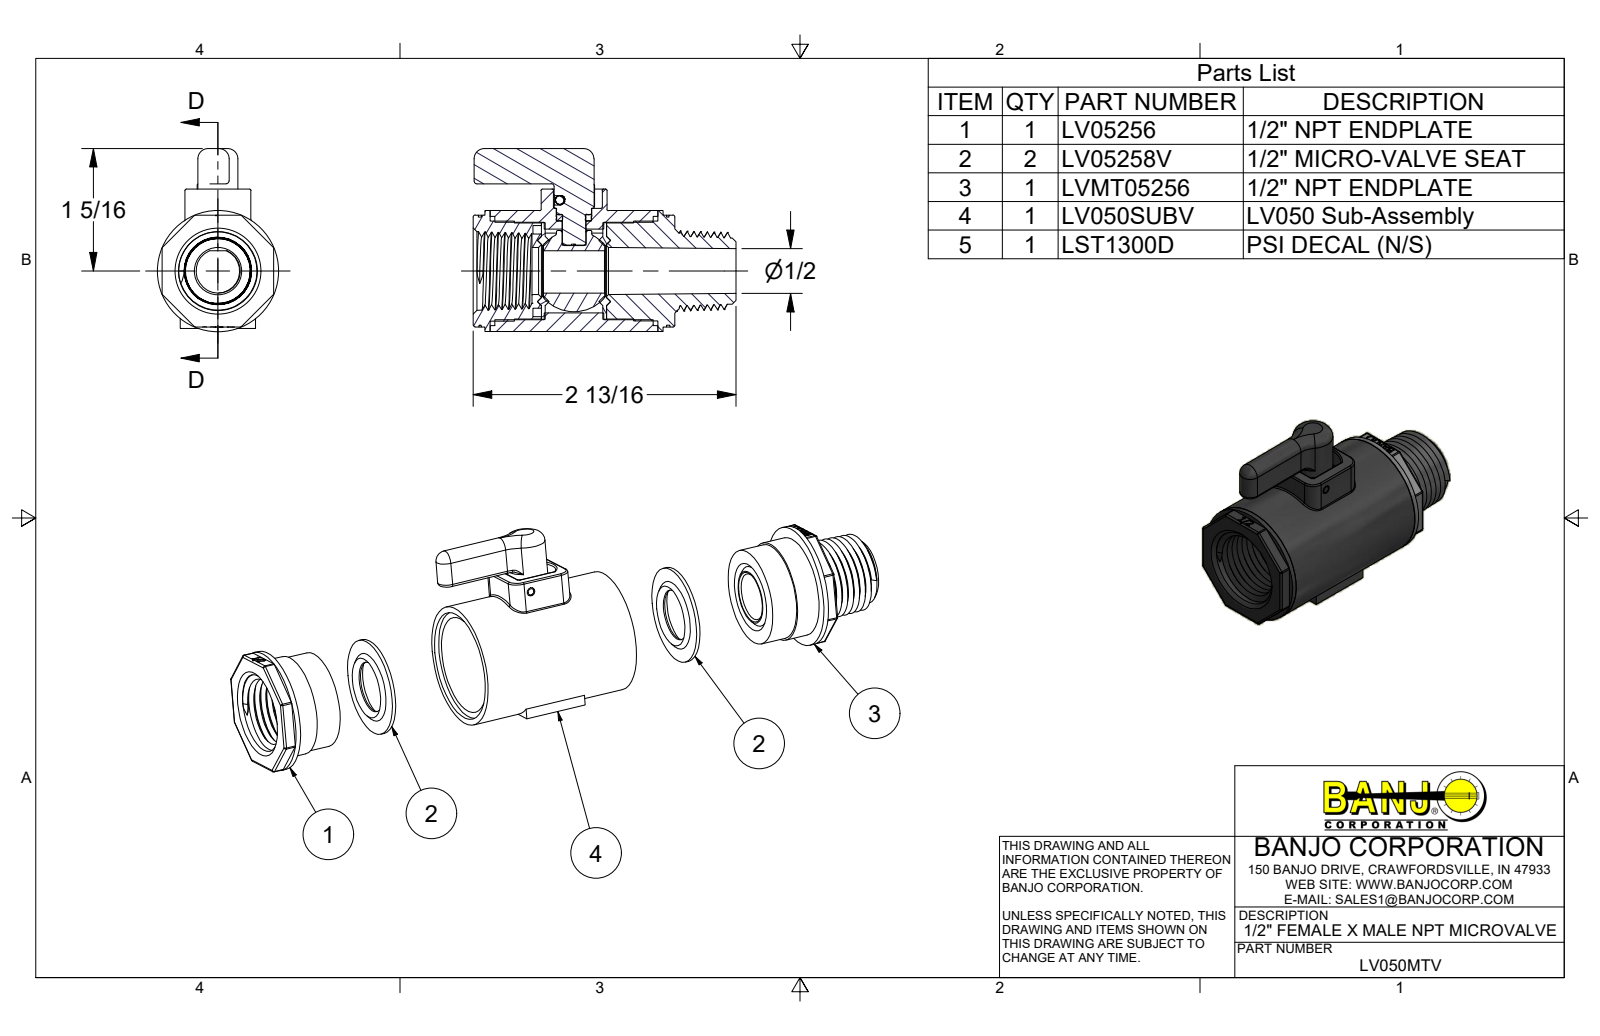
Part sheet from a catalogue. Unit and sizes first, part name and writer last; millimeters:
Units: millimetres
Overall size (bounding box): 70.9 × 49.4 × 32.6
Round holes (diameter × count): ⌀2.3 ×4, ⌀2.4 ×1, ⌀6.4 ×1, ⌀9.3 ×1, ⌀9.6 ×1, ⌀11.9 ×1, ⌀12.7 ×1, ⌀13.7 ×1, ⌀22.6 ×1, ⌀26.3 ×1, ⌀29.5 ×1
Round bosses / shafts (diameter × count): ⌀32.6 ×1, ⌀27 ×1, ⌀26 ×1, ⌀25.9 ×1, ⌀10.8 ×1, ⌀9.5 ×1, ⌀9.4 ×1, ⌀6.4 ×1
Partial cylindrical surfaces — rounded edges, fillets, slot ends (radius × count): R0.5 ×24, R0.3 ×16, R0.4 ×14, R3.2 ×4, R0.8 ×2, R1.3 ×2, R2.8 ×2, R6.4 ×2
Main face-to-face distances: 13.8, 31.4, 4.6, 18.4, 36, 49.8, 19.4, 35, 14.9, 30.4
Hole centre spacings: 11.2, 15.7, 22.3
Volume: 41 120 mm³ · Surface area: 26 730 mm²
Bodies: 9 solids, 658 faces (276 planar, 134 cylindrical, 248 other)
Part name (STEP PRODUCT): LV050MTV; LV050SUBV; LV05254A; LV02153B (+6 more)
STEP written by: Autodesk Inventor 2012 (AUTOMOTIVE_DESIGN)
